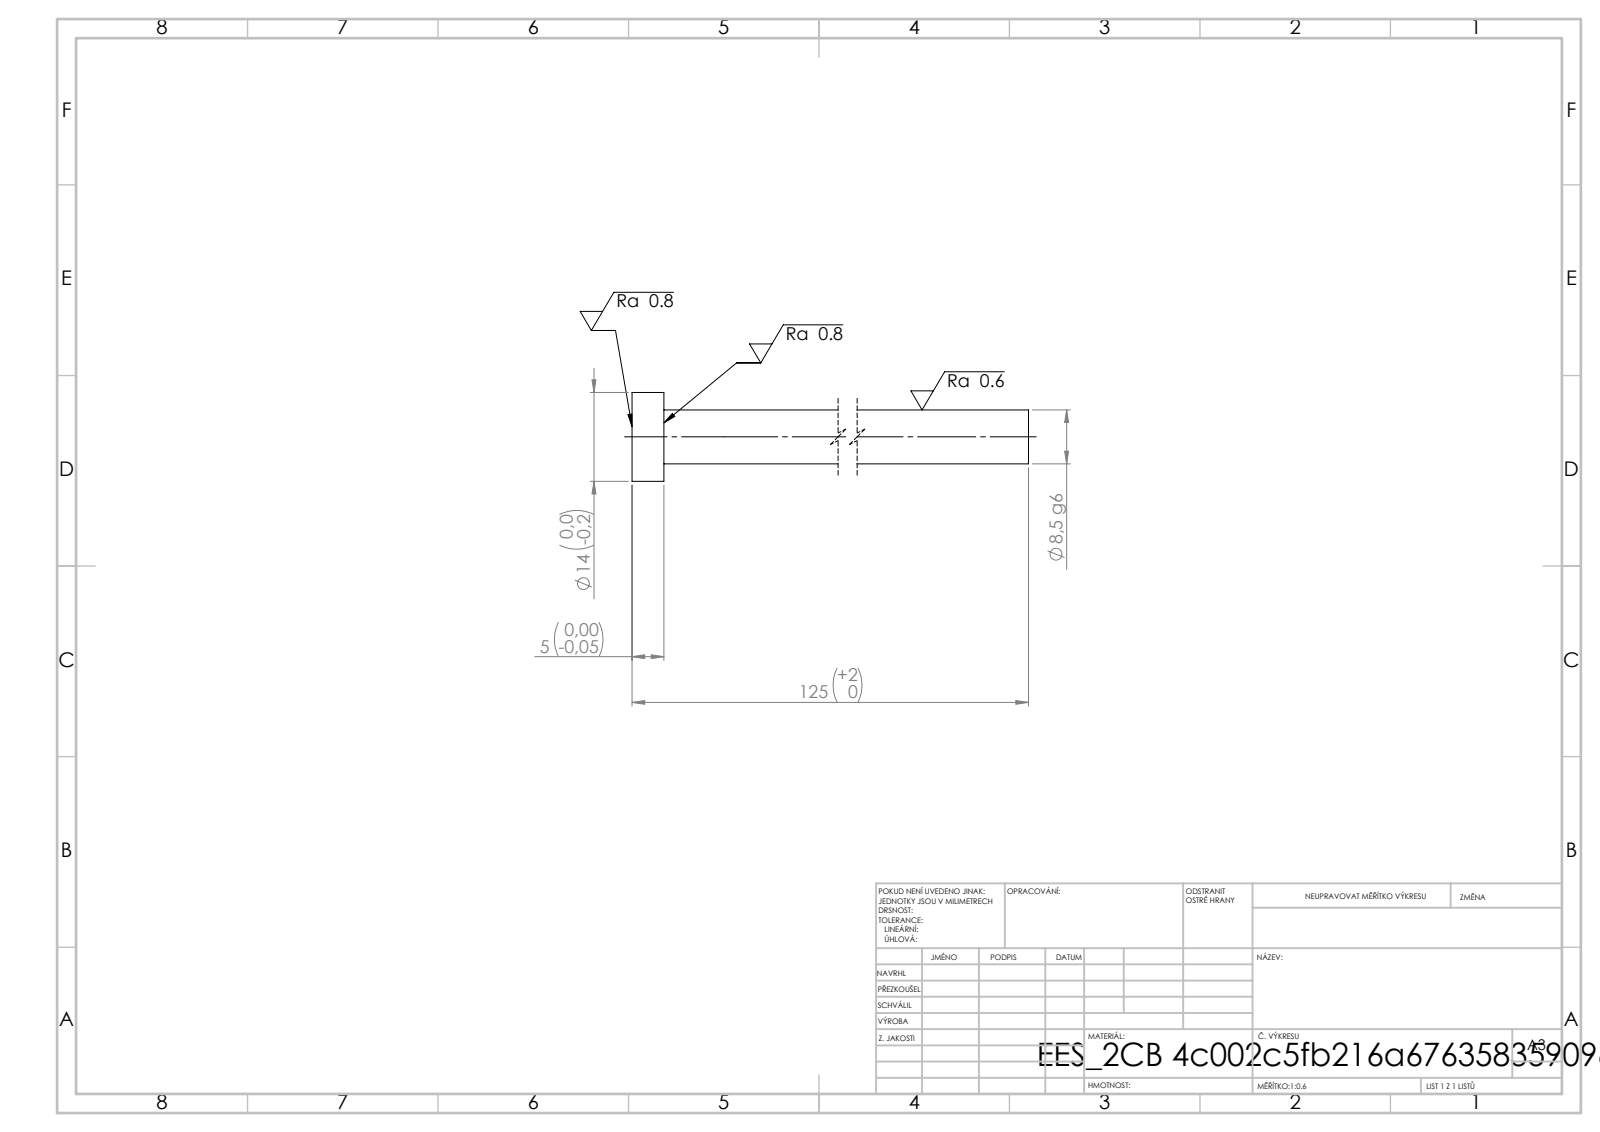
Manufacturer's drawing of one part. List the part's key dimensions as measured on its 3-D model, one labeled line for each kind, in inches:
STEP written by: SolidWorks 2019 (CONFIG_CONTROL_DESIGN)
Units: inches
Bodies: 1 solid, 7 faces (3 planar, 4 cylindrical, 0 other)
Overall size (bounding box): 4.921 × 0.551 × 0.551
Volume: 0.462 in³ · Surface area: 5.785 in²
Round bosses / shafts (diameter × count): ⌀0.551 ×1, ⌀0.335 ×1
Main face-to-face distances: 0.197, 4.921, 4.724
